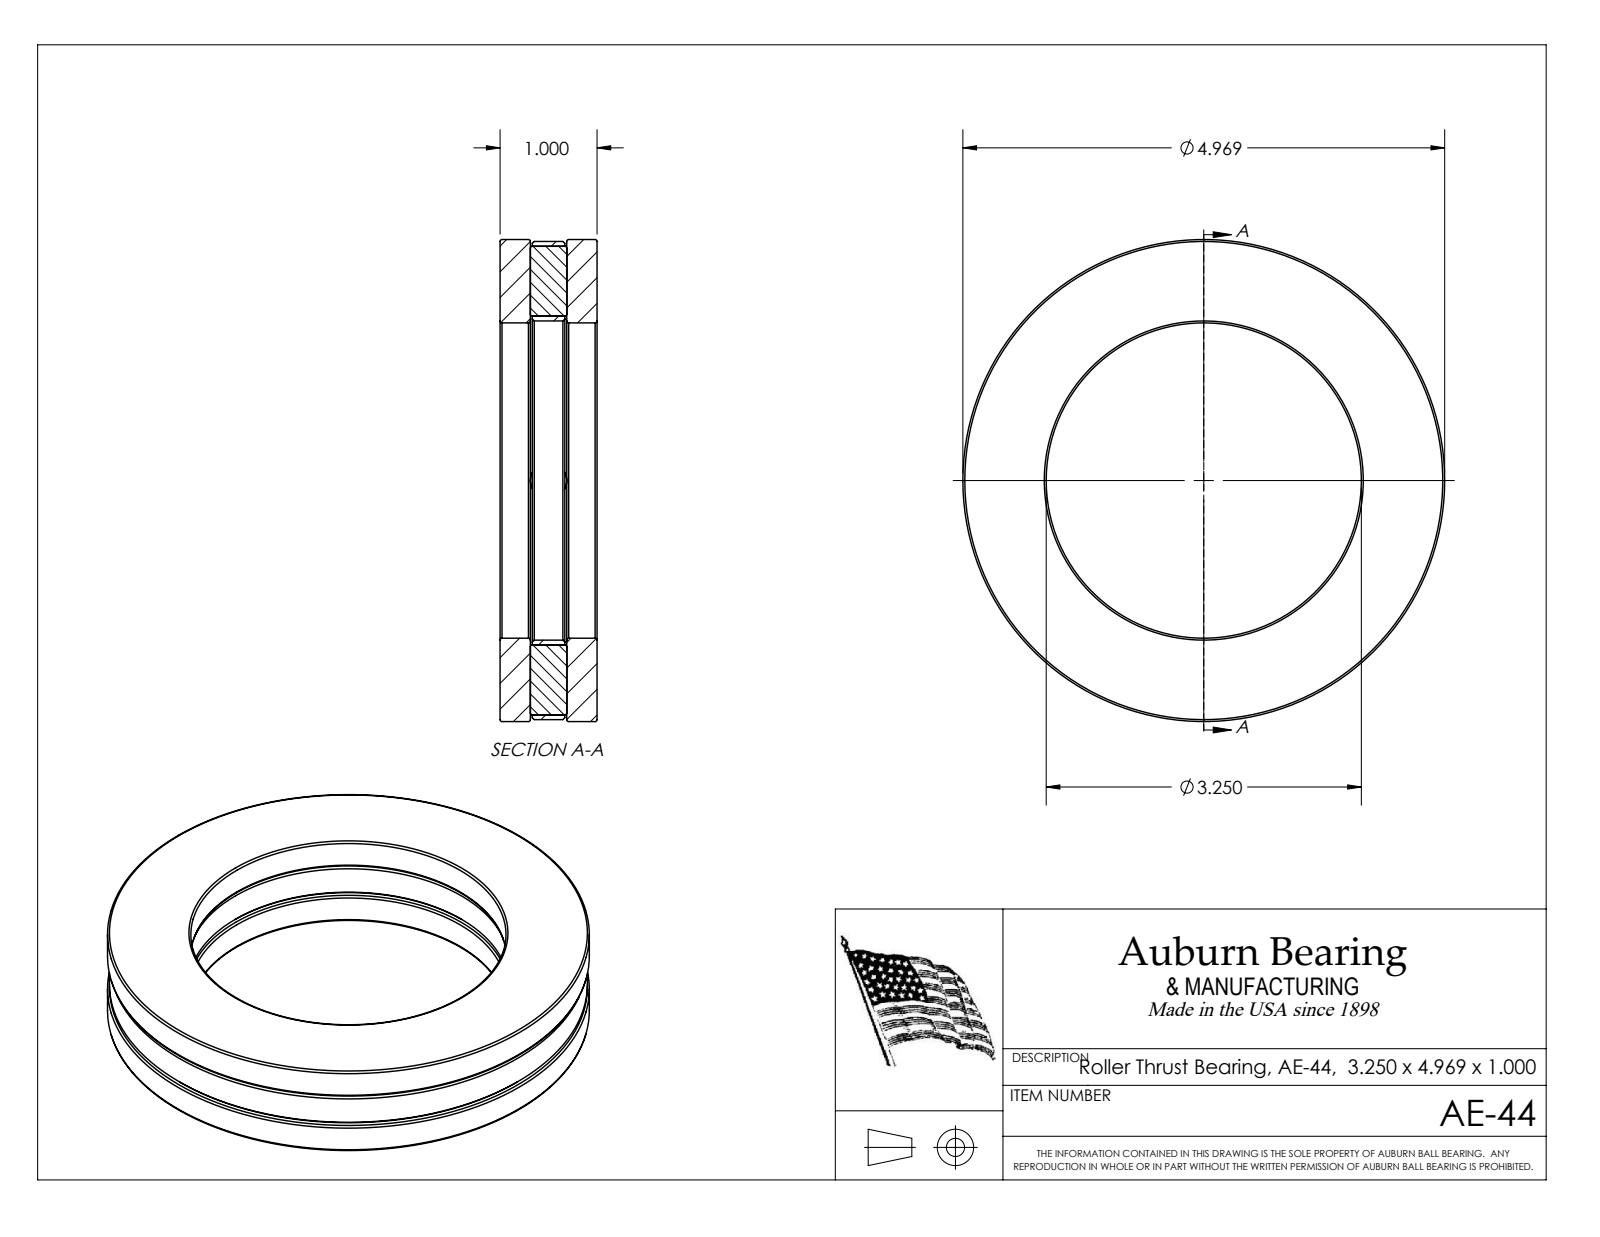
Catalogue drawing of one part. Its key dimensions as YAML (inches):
part_name: "AE-44"
step_written_by: "SolidWorks 2017 (CONFIG_CONTROL_DESIGN)"
units: inches
bodies: {solids: 7, faces: 60, planar: 30, cylindrical: 10, other: 20}
overall_size: [4.969, 4.969, 1]
volume: 10.41
surface_area: 93.8
round_holes:
  - {diameter: 3.25, count: 1}
  - {diameter: 3.29, count: 1}
round_bosses_or_shafts:
  - {diameter: 0.375, count: 2}
  - {diameter: 4.969, count: 1}
  - {diameter: 4.929, count: 1}
face_to_face_distances: [0.313, 0.687, 0.333, 0.667, 0.02, 0.355, 0.375, 1, 0.335, 1.507]
